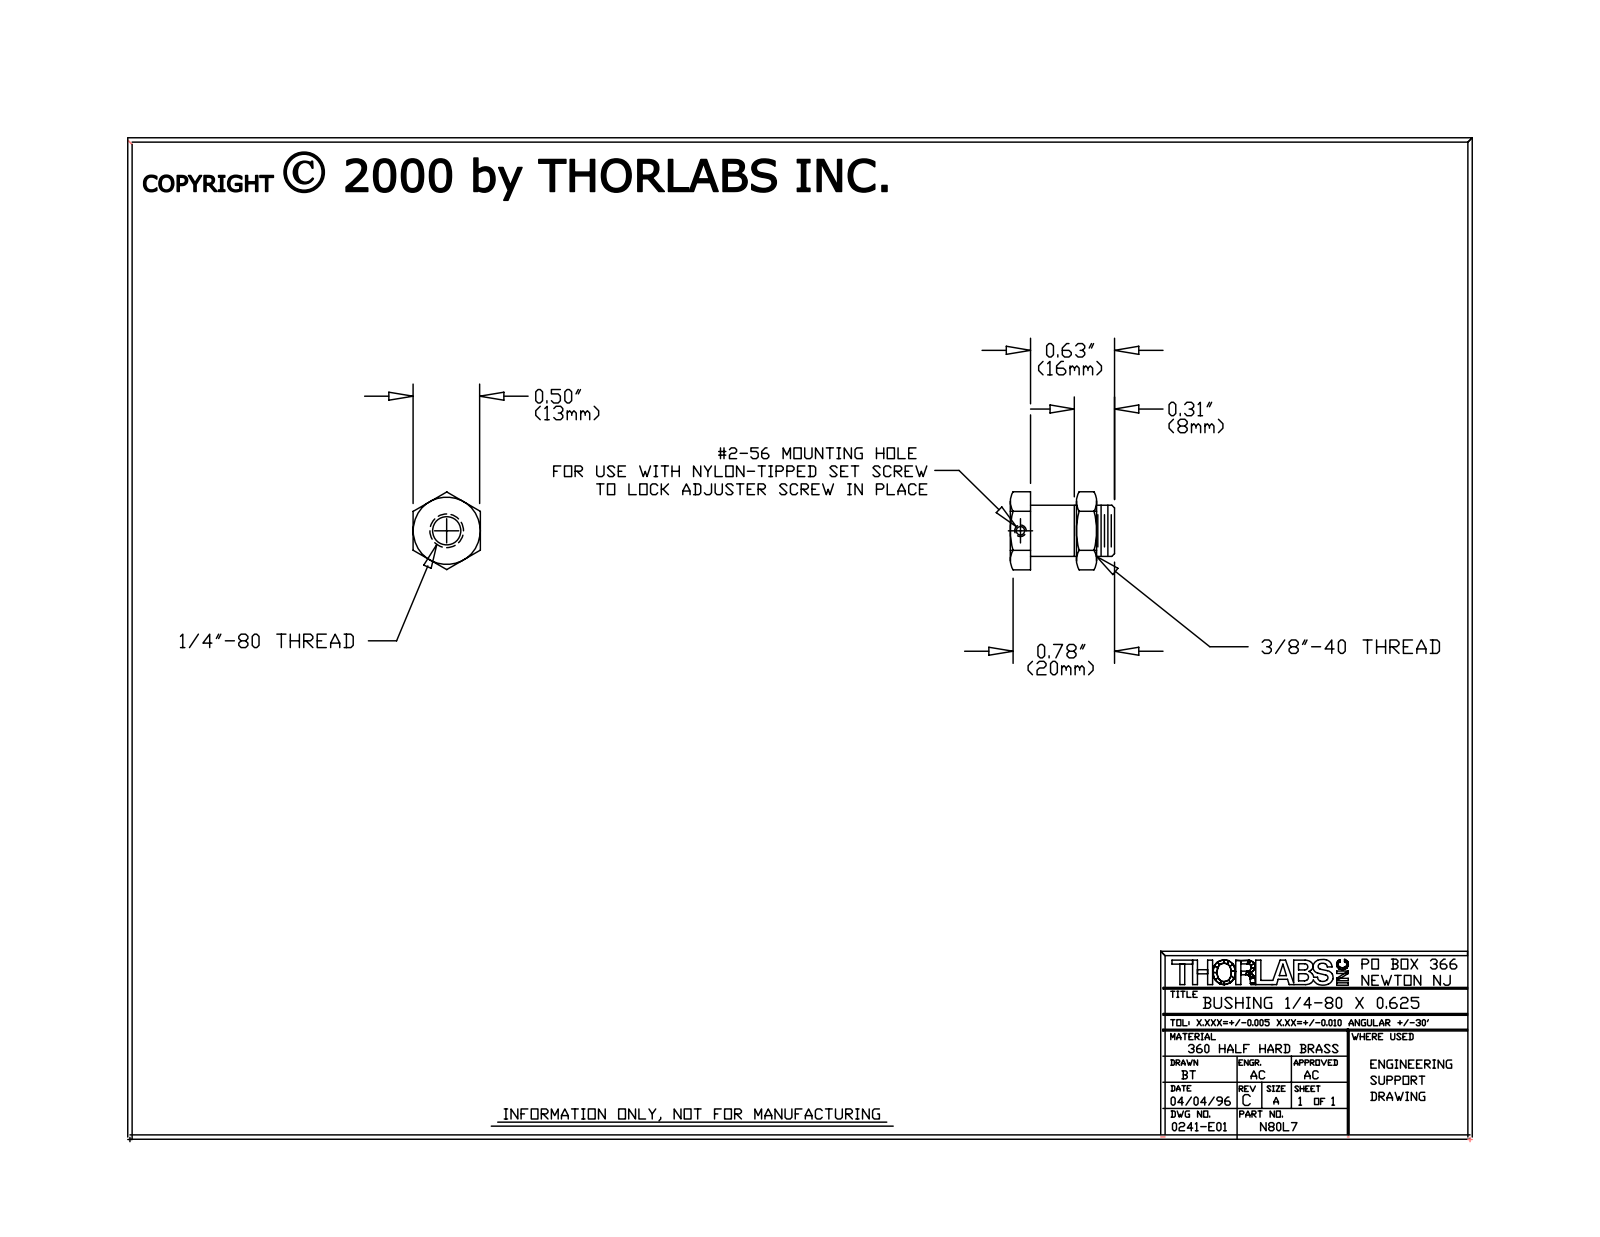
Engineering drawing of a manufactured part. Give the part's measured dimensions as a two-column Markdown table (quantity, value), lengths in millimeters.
| quantity | value |
| --- | --- |
| part name | 0241-E0W |
| STEP written by | SolidWorks 2007 (AUTOMOTIVE_DESIGN) |
| units | millimeters |
| bodies | 3 solids, 68 faces (28 planar, 16 cylindrical, 24 other) |
| overall size | 19.7 × 14.7 × 12.7 |
| volume | 1 400 mm³ |
| surface area | 1 630 mm² |
| round holes (diameter × count) | 2.2 × 1, 5.3 × 1, 8.8 × 1 |
| round bosses / shafts (diameter × count) | 9.5 × 1, 9.5 × 1, 8.9 × 1, 1.4 × 1 |
| main face-to-face distances | 12.7, 3.8, 3.2, 10.8, 14.7, 14, 17.8, 12.7, 1.9, 5 |
